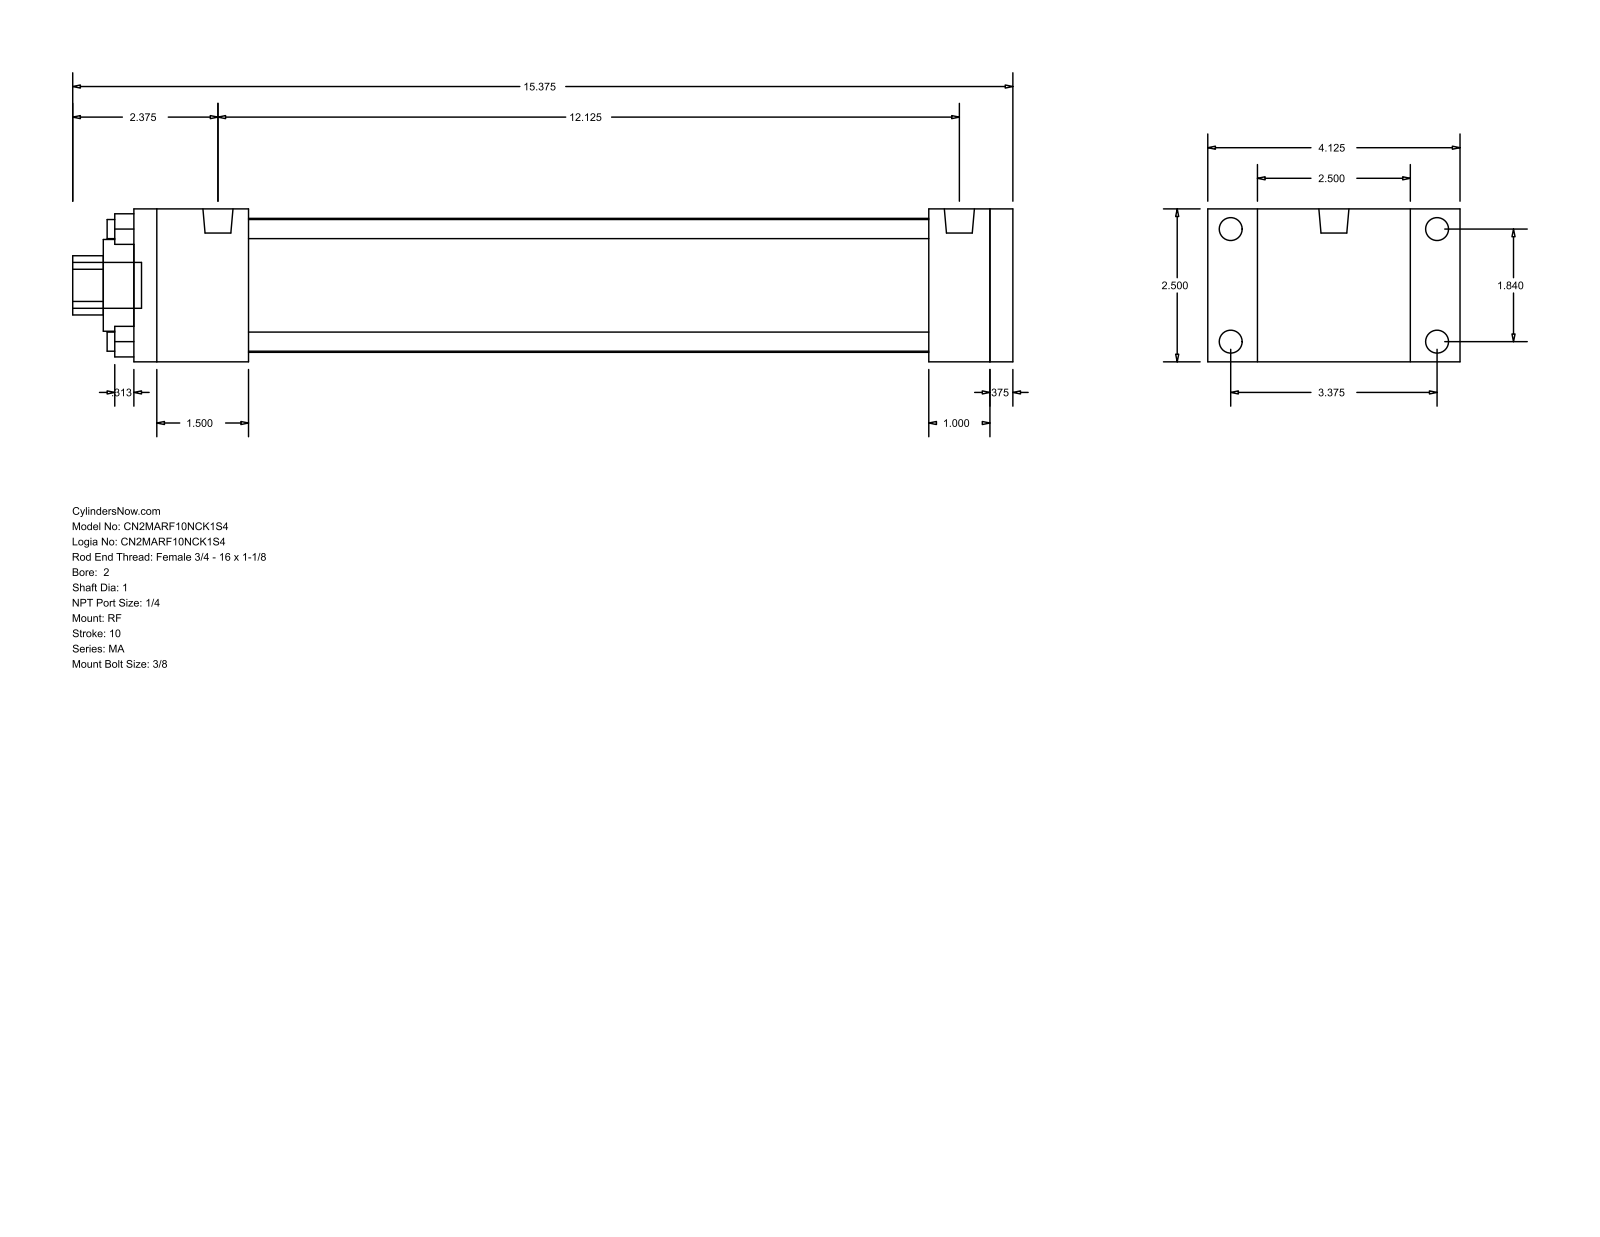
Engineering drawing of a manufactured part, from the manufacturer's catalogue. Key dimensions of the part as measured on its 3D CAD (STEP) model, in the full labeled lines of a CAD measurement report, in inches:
Part name (STEP PRODUCT): MA_RF__0200_1
STEP written by: GSSL Pune (CONFIG_CONTROL_DESIGN)
Units: inches
Bodies: 0 solids, 92 faces (64 planar, 28 cylindrical, 0 other)
Overall size (bounding box): 15.375 × 4.125 × 2.5
Round holes (diameter × count): ⌀0.313 ×4, ⌀1 ×1, ⌀1.5 ×1, ⌀2.19 ×1
Round bosses / shafts (diameter × count): ⌀0.375 ×4, ⌀0.313 ×4, ⌀0.492 ×2, ⌀0.75 ×1
Partial cylindrical surfaces — rounded edges, fillets, slot ends (radius × count): R0.484 ×1
Main face-to-face distances: 2.5, 14, 0.375, 14.375, 1, 0.813, 0.5, 1.875, 12.125, 12.5
Hole centre spacings: 1.301, 1.84, 2.602
